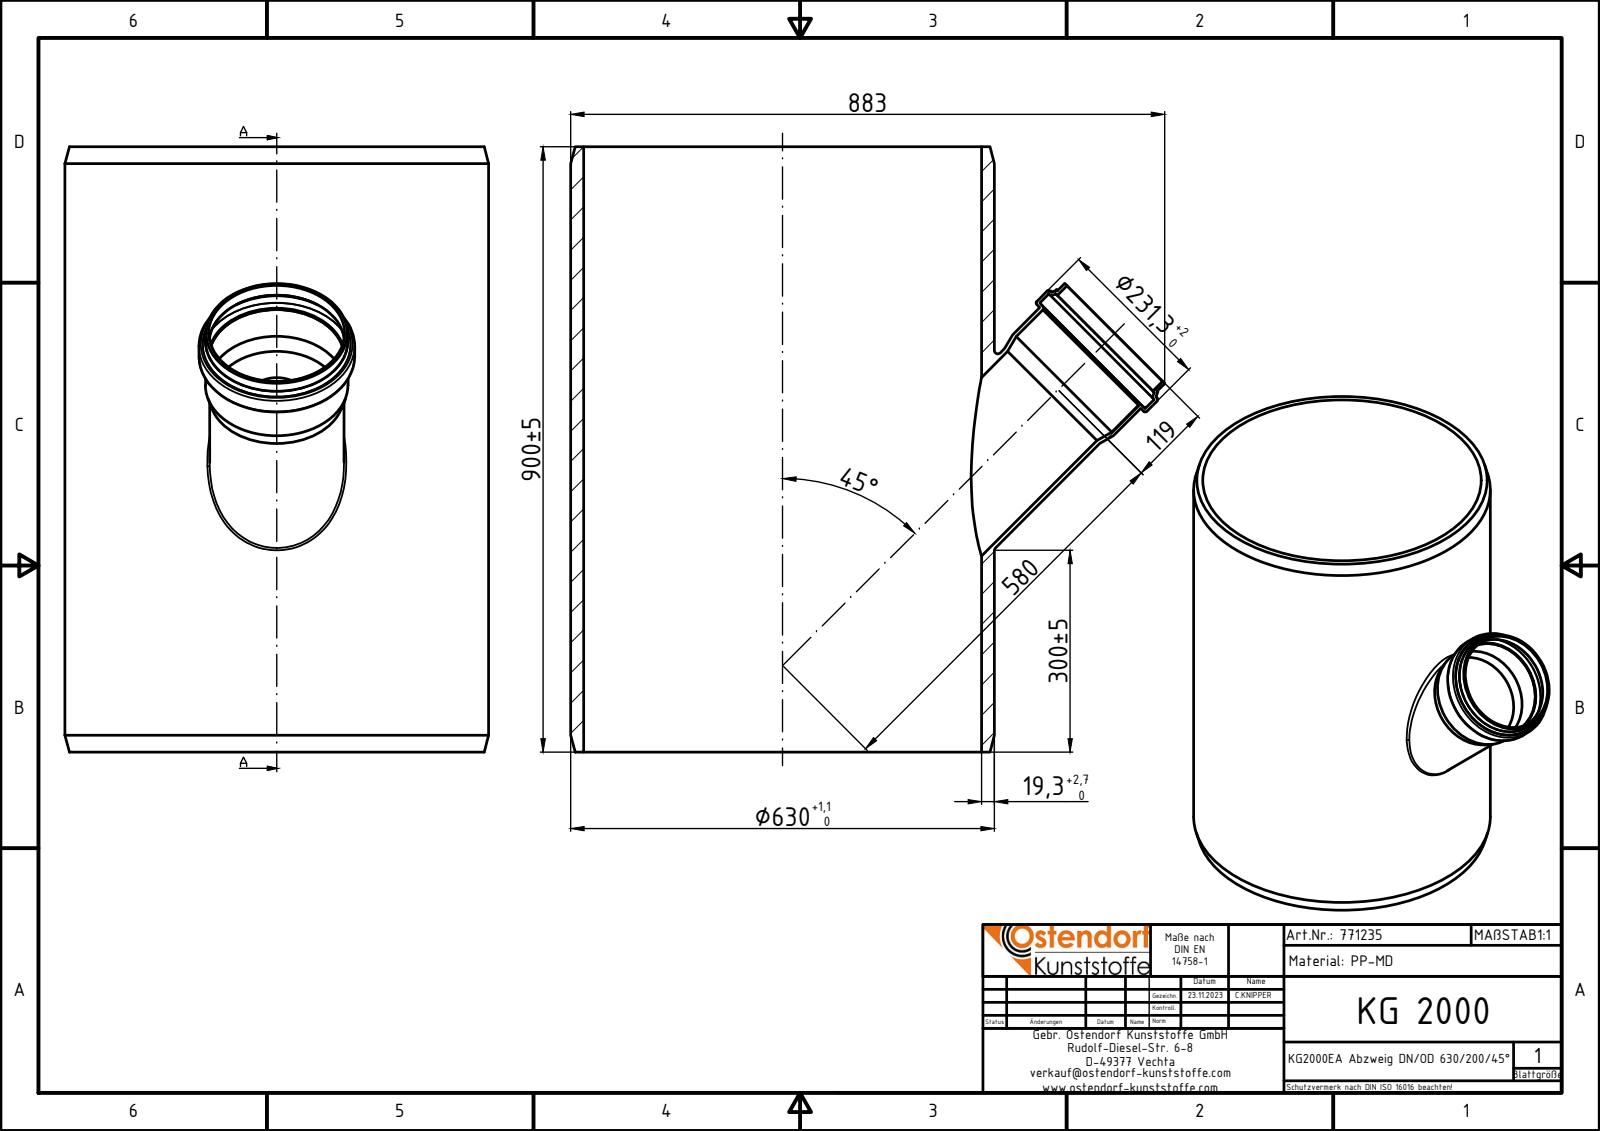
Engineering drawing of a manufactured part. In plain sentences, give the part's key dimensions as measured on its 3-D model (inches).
The part is named "771235z". Its 3-D file was written by "Autodesk Inventor 2024 (AUTOMOTIVE_DESIGN)". It is 1 solid with 42 faces: 7 planar, 11 cylindrical and 24 other. Overall it measures 35.433 by 34.764 by 24.803 inches. Its volume is 2 029 cubic inches and its surface area 5 878 square inches. Round holes: 2 of diameter 7.913, 1 of diameter 7.386, 1 of diameter 7.906, 1 of diameter 8.736, 1 of diameter 23.283. Round bosses or shafts: 1 of diameter 24.803, 1 of diameter 9.106, 1 of diameter 8.346, 1 of diameter 8.283, 1 of diameter 7.874. The main face-to-face distances are 35.433, 1.11, 2.035, 0.925, 1.404, 0.294, 0.631, 0.04, 1.07, 1.365.
